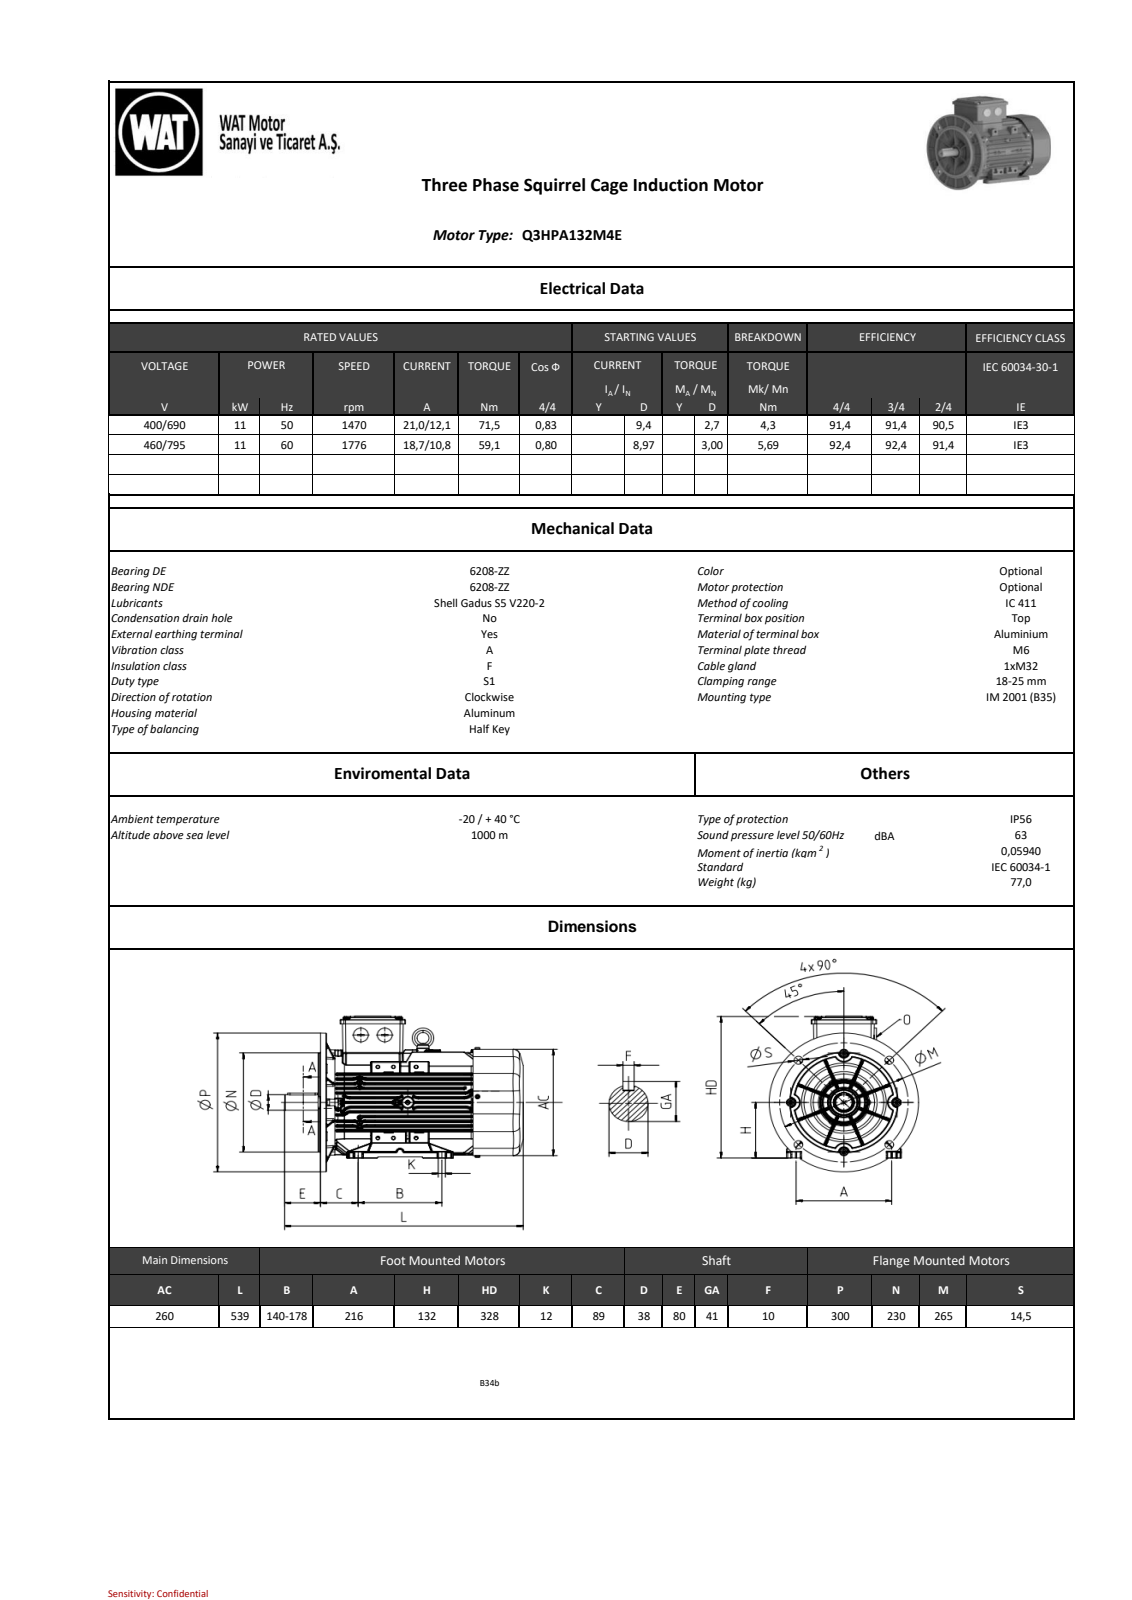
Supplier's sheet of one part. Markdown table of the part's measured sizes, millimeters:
| quantity | value |
| --- | --- |
| part name | QH series_ 132_B35 _DEEP COVER__stp_objects |
| STEP written by | SIEMENS PLM Software NX2206.8101 (AP203_CONFIGURATION_CONTROLLED_3D_DESIGN_OF_MECHANICAL_PARTS_AND_ASSEMBLIES_MIM_LF) |
| units | millimeters |
| bodies | 0 solids, 8157 faces (2041 planar, 3540 cylindrical, 2576 other) |
| overall size | 538.95 × 340.18 × 299.95 |
| round holes (diameter × count) | 8.48 × 1, 8.48 × 1, 12 × 1, 13 × 1, 34.5 × 1, 62 × 1, 82 × 1, 180 × 1, 225 × 1 |
| round bosses / shafts (diameter × count) | 8 × 8, 13 × 4, 38 × 3, 230.5 × 1, 230 × 1, 86.77 × 1, 40 × 1, 37.4 × 1 |
| partial cylindrical surfaces (radius × count) | 1 × 1099, 0.8 × 963, 0.5 × 102, 3 × 66, 2 × 65, 1.5 × 57, 5 × 20, 60 × 16 |
| main face-to-face distances | 10.42, 1.5, 10.56, 10.28, 20.84, 125.58, 115.18, 104.9, 9.5, 4.5 |
| hole center spacings | 0.67, 178.91 |
